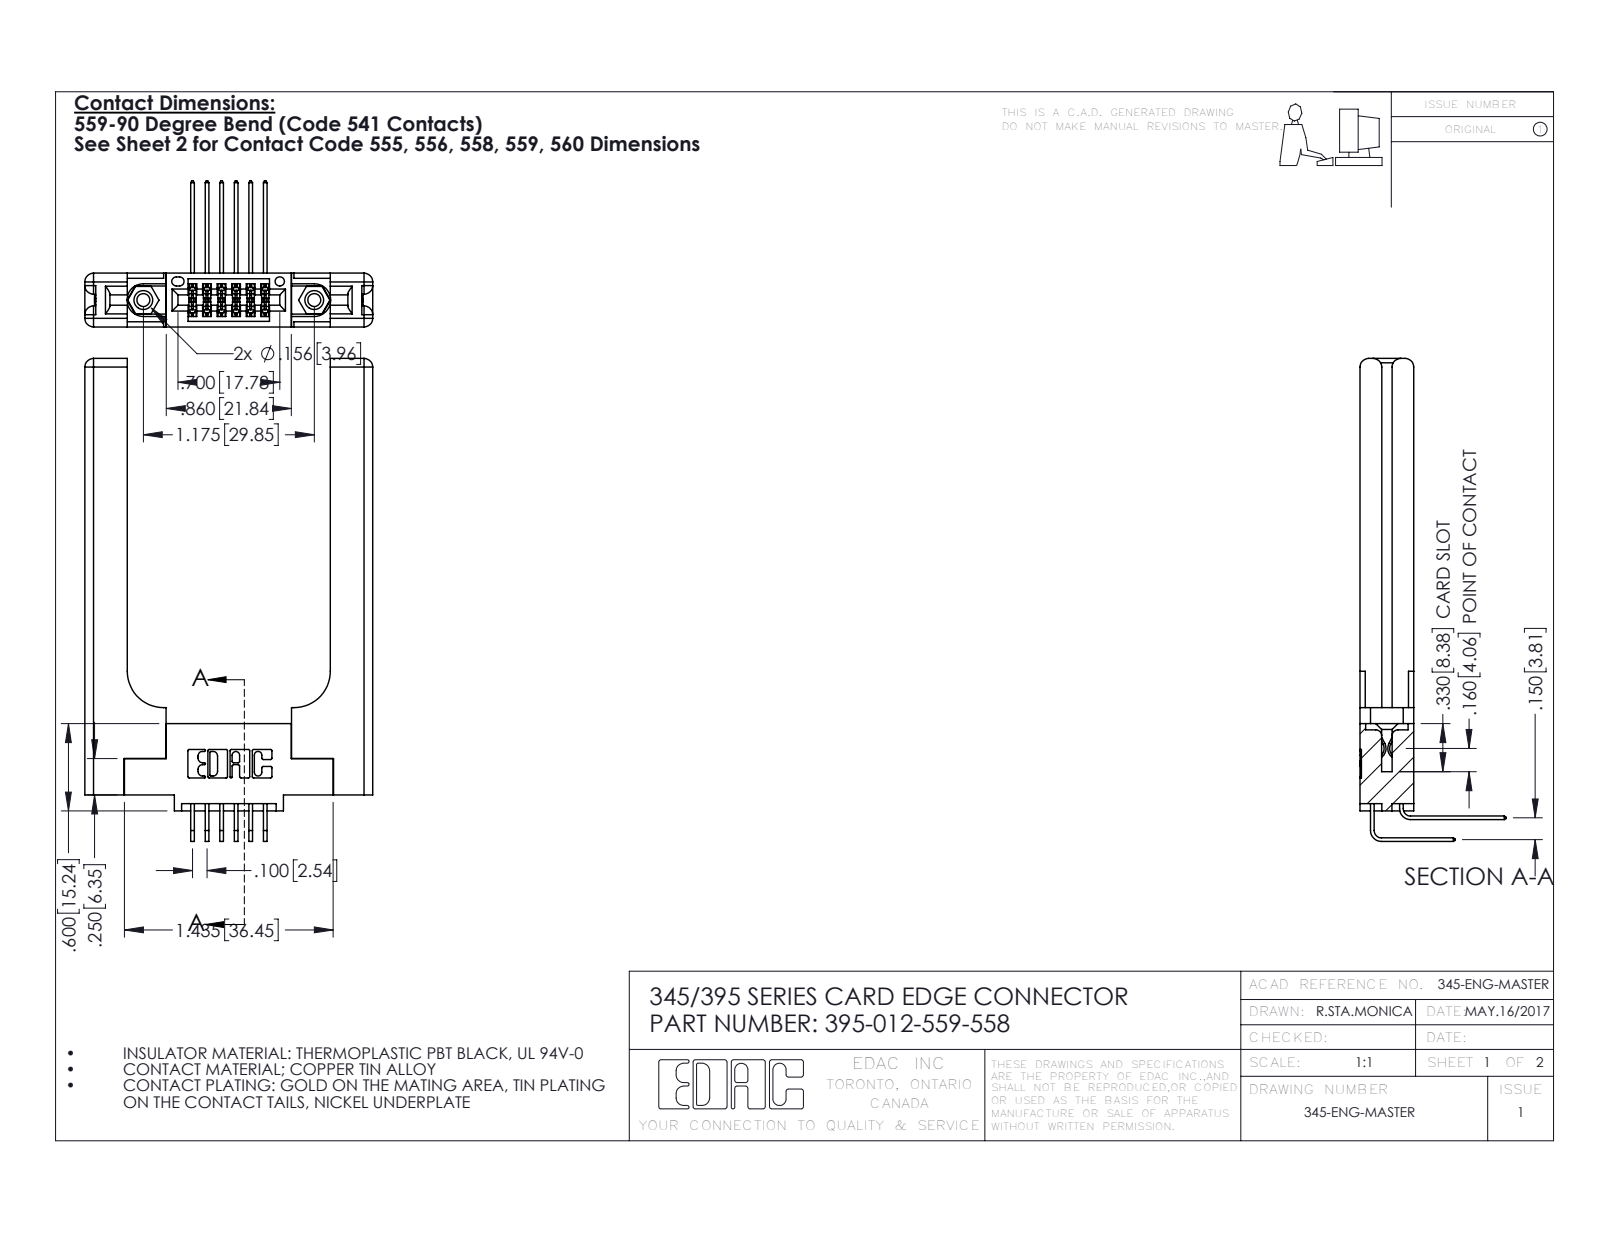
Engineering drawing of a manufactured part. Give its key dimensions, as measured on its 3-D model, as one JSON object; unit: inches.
{"part_name": "345-250-001_345-250-001-102; 395-012-559-558; 345-292-001_558 559 Tail - 1; 345-220-058_345-220-058 (+2 more)", "step_written_by": "SolidWorks 2016 (CONFIG_CONTROL_DESIGN)", "units": "inches", "bodies": {"solids": 17, "faces": 1010, "planar": 652, "cylindrical": 298, "other": 60}, "overall_size": [3.319, 1.979, 1.005], "volume_in3": 0.795, "surface_area_in2": 17.82, "round_holes": [[0.089, 2], [0.125, 2], [0.156, 2], [0.064, 1]], "round_bosses_or_shafts": [[0.155, 2]], "partial_cylinders_radius": [[0.01, 22], [0.006, 19], [0.06, 16], [0.007, 6], [0.031, 6], [0.026, 3], [0.014, 2], [0.019, 2]], "face_to_face_distances": [0.37, 0.15, 0.22, 0.072, 0.148, 0.077, 0.298, 1.396, 0.071, 0.292], "hole_center_spacings": [0.27, 0.946, 1.175]}
